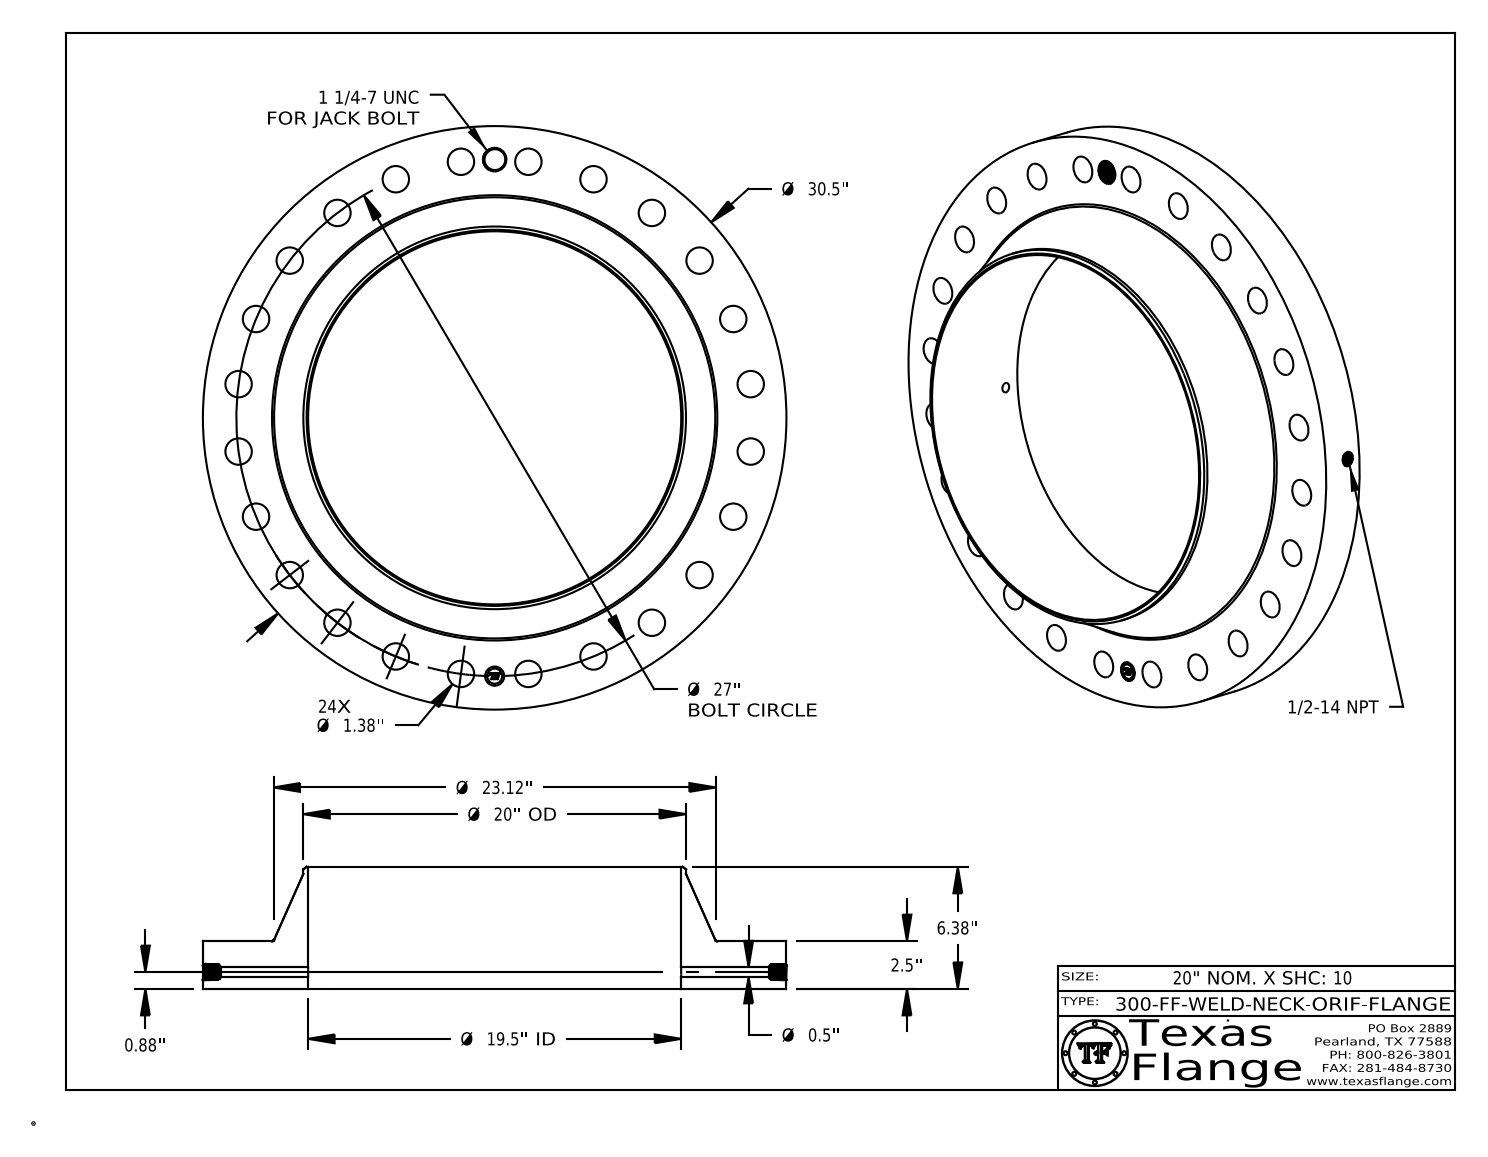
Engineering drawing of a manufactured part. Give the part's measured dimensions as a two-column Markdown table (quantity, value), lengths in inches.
| quantity | value |
| --- | --- |
| part name | 300-FF-WELD-NECK |
| STEP written by | CATIA V5 STEP AP214 (AUTOMOTIVE_DESIGN) |
| units | inches |
| bodies | 1 solid, 815 faces (368 planar, 129 cylindrical, 318 other) |
| overall size | 30.5 × 30.5 × 6.38 |
| volume | 1 226 in³ |
| surface area | 1 885 in² |
| round holes (diameter × count) | 1.38 × 24, 0.5 × 1, 0.672 × 1, 1 × 1, 1.109 × 1, 19.5 × 1 |
| round bosses / shafts (diameter × count) | 0.061 × 8, 30.5 × 1, 20 × 1, 0.788 × 1 |
| main face-to-face distances | 2.5, 6.38, 3.88, 2.485, 0.015, 3.895, 0.298, 0.293, 0.054, 0.248 |
| hole center spacings | 13.5, 23.383, 24.945, 21.42, 3.524, 6.988, 19.092, 26.08 |
